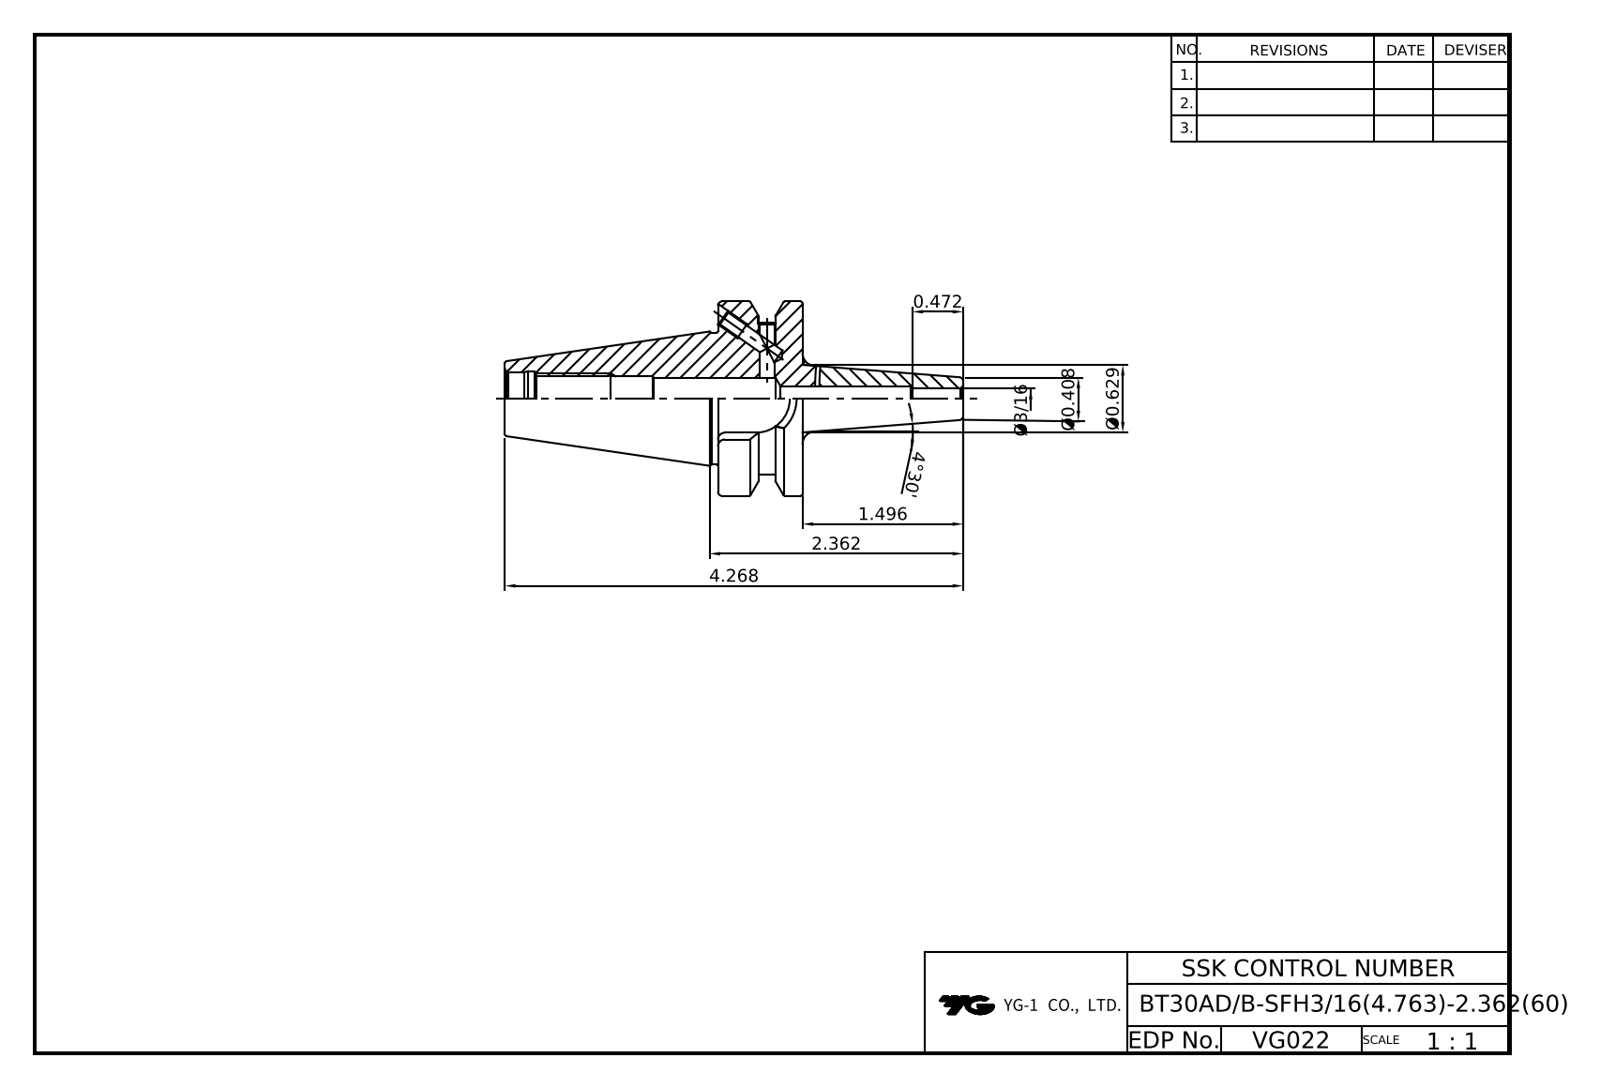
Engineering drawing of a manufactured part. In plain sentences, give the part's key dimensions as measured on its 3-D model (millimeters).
The part is named "LO-BT30-SFH4.7625-2.36". Its 3-D file was written by "Autodesk Inventor 2025 (AUTOMOTIVE_DESIGN)". It is 1 solid with 47 faces: 15 planar, 13 cylindrical and 19 other. Overall it measures 108.4 by 46 by 46 millimeters. Its volume is 51 592 cubic millimeters and its surface area 14 335 square millimeters. Round holes: 1 of diameter 4.76, 1 of diameter 6, 1 of diameter 10.11, 1 of diameter 12.5, 1 of diameter 13.1. Round bosses or shafts: 1 of diameter 46, 1 of diameter 31.2. Partial cylindrical surfaces (rounded edges, fillets, slot ends): 1 of radius 8.05, 1 of radius 18.8. The main face-to-face distances are 20, 32.6, 16.1, 50.4, 70.4, 64, 13.6, 6.4, 60, 9.6.
